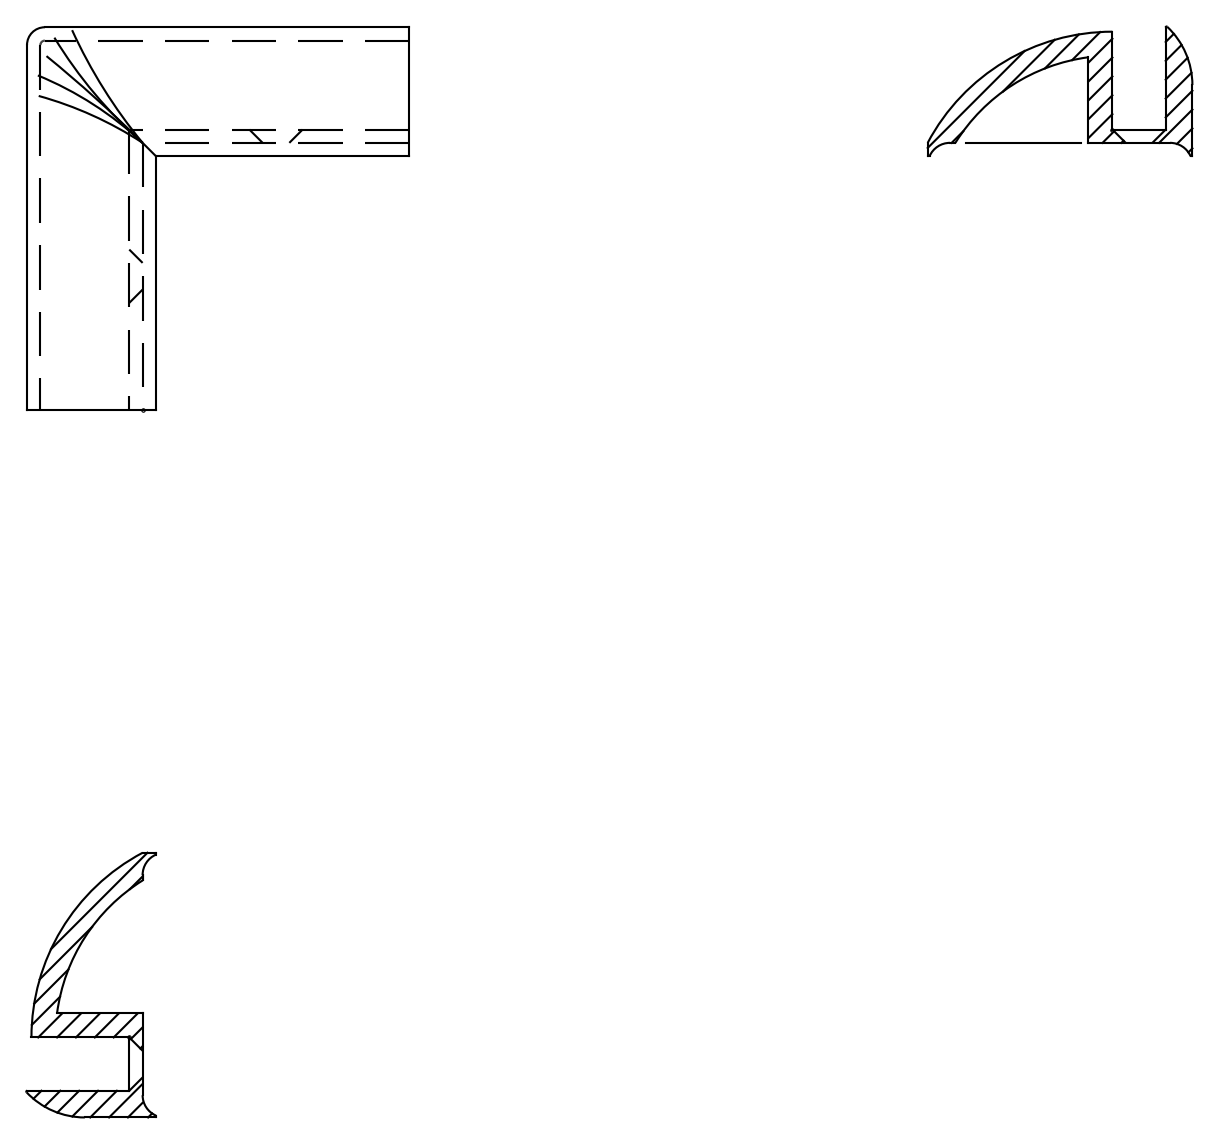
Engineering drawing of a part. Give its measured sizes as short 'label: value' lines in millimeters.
written by: THINKDESIGN (CONFIG_CONTROL_DESIGN)
unit: mm
bodies: 1 solid, 33 faces (19 planar, 10 cylindrical, 4 other)
size: 43.21 × 43.21 × 29.77
volume: 9 511 mm³; area: 8 391 mm²
rounds: 4× R2.5, 2× R9, 2× R20.8, 2× R23.5
face distances: 6, 8.7, 2.7, 3, 9, 11.7, 1.5, 31.5, 30, 29.77
